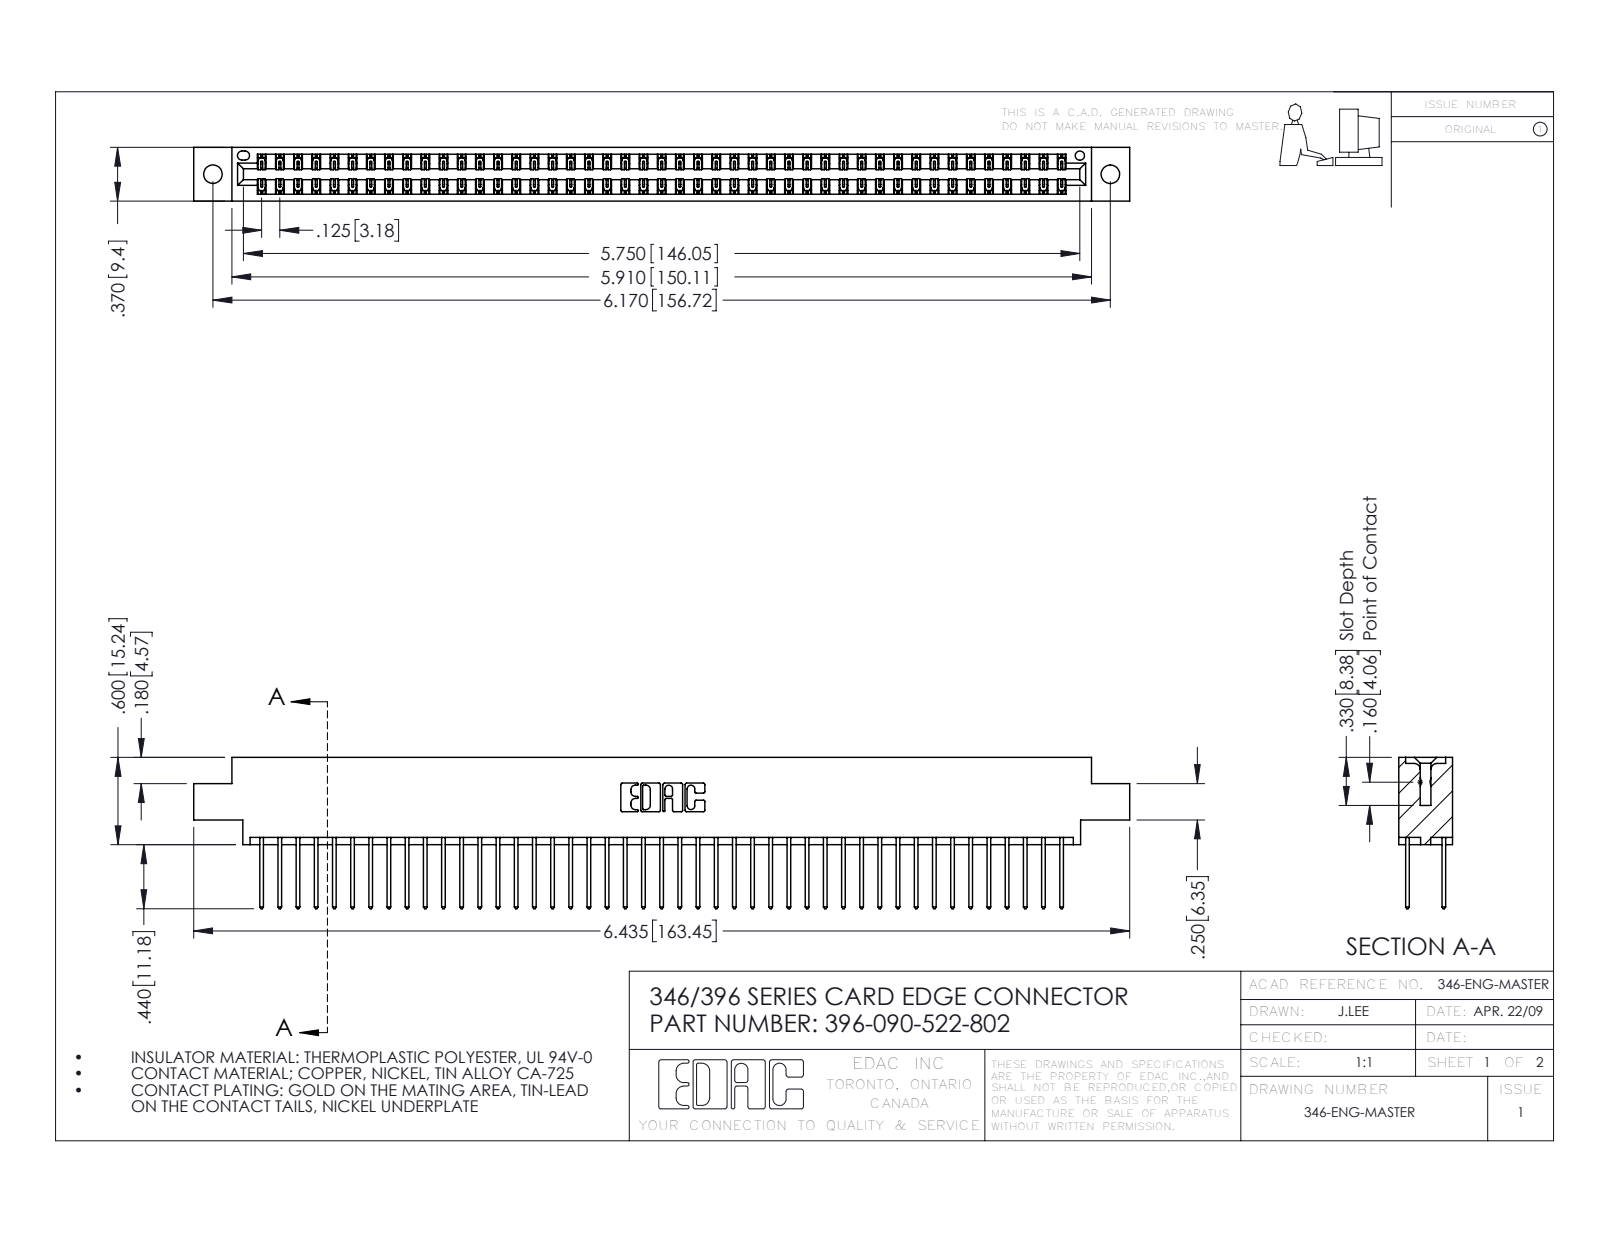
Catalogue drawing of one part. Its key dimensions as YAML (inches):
part_name: "346 Part_0.170 Offset - 0.128 Dia; 345-292-001_345-293-122; 396-090-522-802"
step_written_by: "SolidWorks 2016 (CONFIG_CONTROL_DESIGN)"
units: inches
bodies: {solids: 91, faces: 4806, planar: 3230, cylindrical: 1576, other: 0}
overall_size: [6.435, 1.04, 0.37]
volume: 0.976
surface_area: 35.68
round_holes:
  - {diameter: 0.128, count: 2}
  - {diameter: 0.064, count: 1}
partial_cylinders:
  - {radius: 0.006, count: 135}
  - {radius: 0.01, count: 90}
  - {radius: 0.01, count: 22}
  - {radius: 0.007, count: 6}
  - {radius: 0.031, count: 6}
  - {radius: 0.026, count: 3}
  - {radius: 0.014, count: 2}
  - {radius: 0.022, count: 2}
face_to_face_distances: [0.048, 0.322, 0.25, 0.37, 0.072, 0.298, 0.025, 0.275, 0.148, 0.222]
hole_center_spacings: [0.246, 5.961, 6.17]
